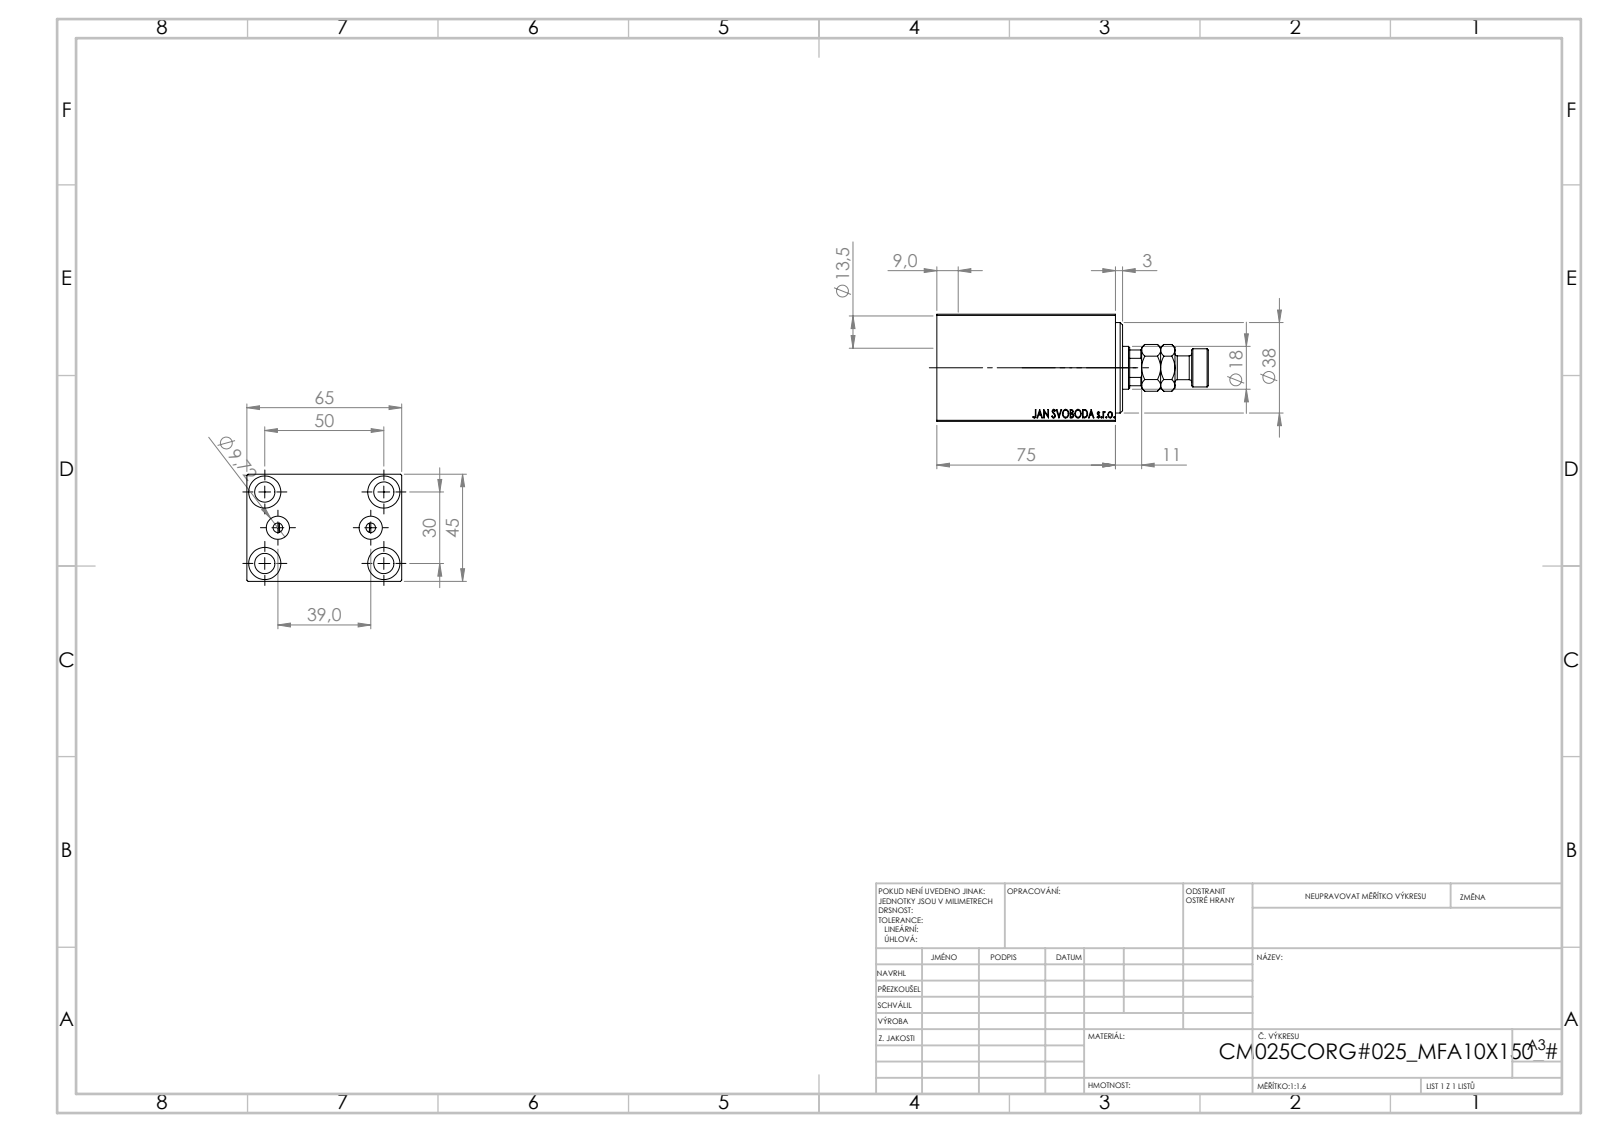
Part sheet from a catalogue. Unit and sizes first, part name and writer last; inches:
Units: inches
Overall size (bounding box): 4.488 × 2.559 × 1.772
Round holes (diameter × count): ⌀0.335 ×5, ⌀0.531 ×4, ⌀0.157 ×2, ⌀0.383 ×2, ⌀0.709 ×1, ⌀0.846 ×1, ⌀0.984 ×1, ⌀1.063 ×1, ⌀1.496 ×1
Round bosses / shafts (diameter × count): ⌀0.63 ×1, ⌀0.394 ×1
Partial cylindrical surfaces — rounded edges, fillets, slot ends (radius × count): R0.335 ×1
Main face-to-face distances: 1.772, 2.559, 0.236, 2.52, 2.717, 2.953, 2.756, 0.197, 0.118, 0.315
Hole centre spacings: 0.629, 1.148, 1.849, 0.768, 1.181, 1.969, 2.296, 1.535
Volume: 12 in³ · Surface area: 79.69 in²
Bodies: 4 solids, 910 faces (424 planar, 60 cylindrical, 426 other)
Part name (STEP PRODUCT): MFA; V450CM_C_VCP; V450CM_VC_B; V450CM_C_Body
STEP written by: SolidWorks 2019 (CONFIG_CONTROL_DESIGN)
